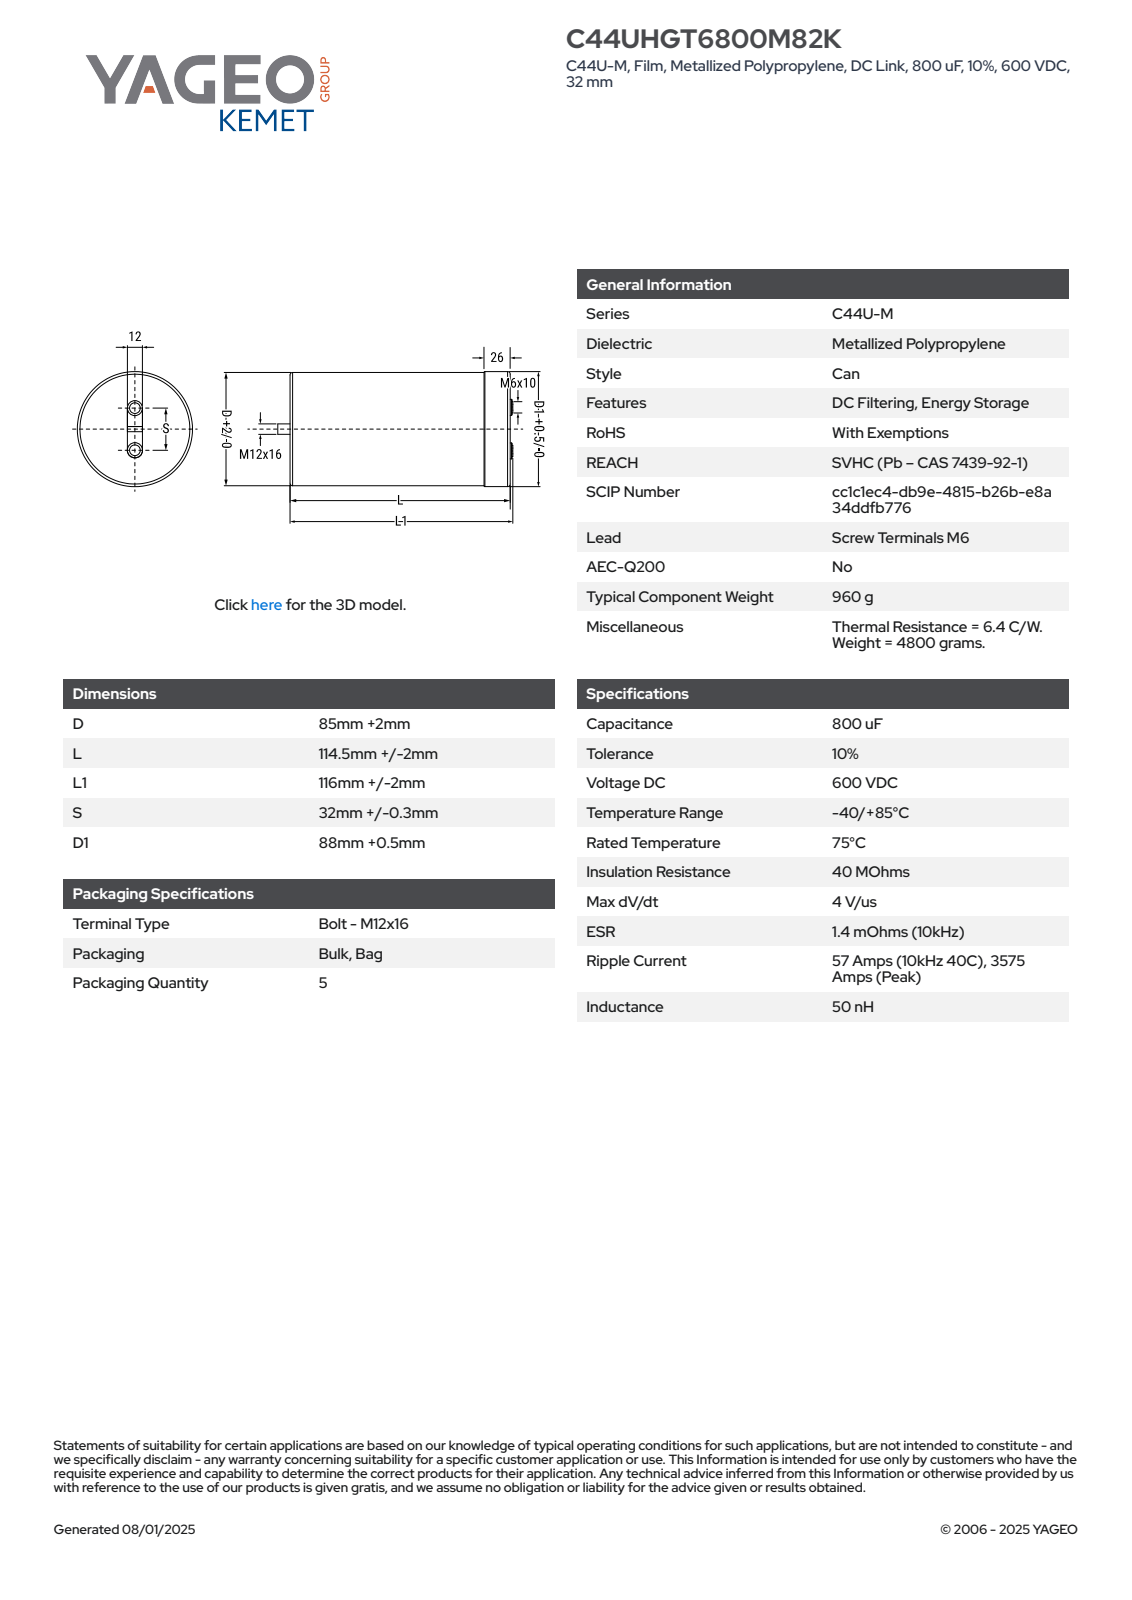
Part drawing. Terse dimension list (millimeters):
name: CFP_C44UMR_85X114.5_D87L116.5S32L1118D188.5
written by: SolidWorks 2014 (AUTOMOTIVE_DESIGN)
unit: mm
bodies: 1 solid, 84 faces (32 planar, 21 cylindrical, 31 other)
size: 134 × 88.5 × 88.5
volume: 699 492 mm³; area: 45 360 mm²
holes: 2× ⌀6
bosses: 3× ⌀12, 2× ⌀10, 1× ⌀88.5, 1× ⌀87
rounds: 1× R43.51
face distances: 116.5, 90.5, 26, 16, 106.5, 132.5, 134, 118, 27.5, 1.5
hole spacings: 32
